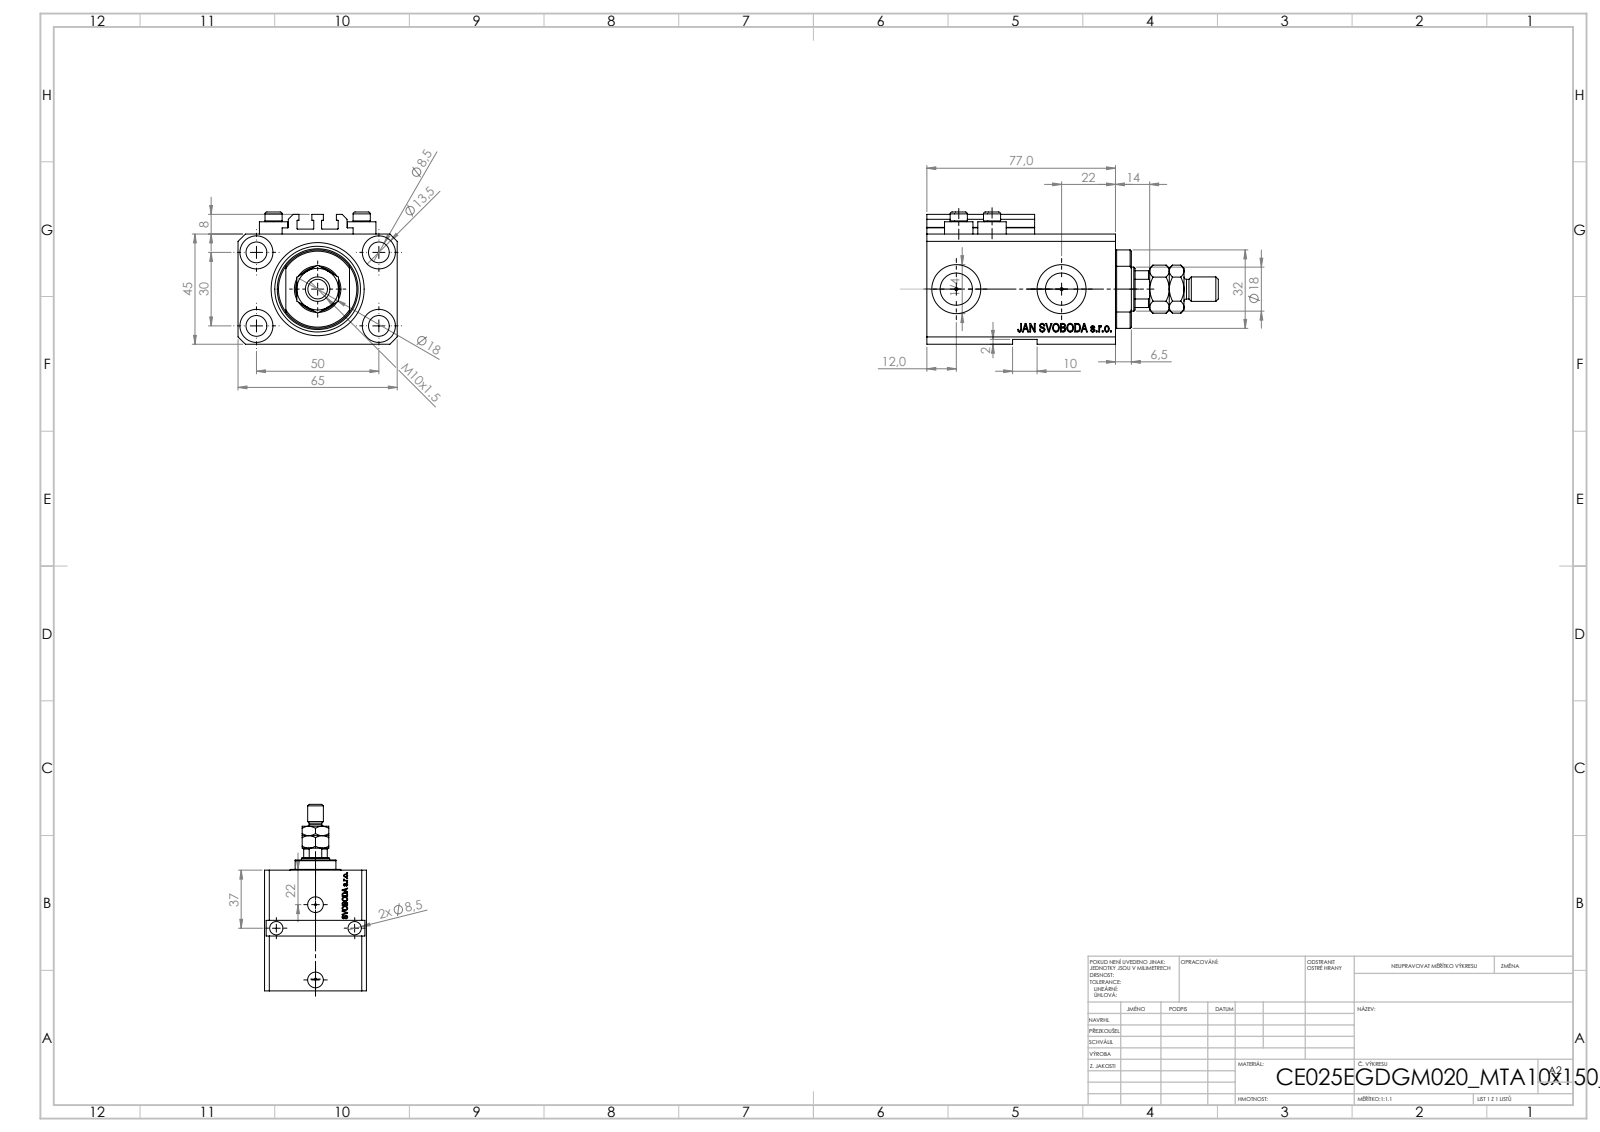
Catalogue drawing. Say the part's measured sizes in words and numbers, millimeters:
The part is named "MTA; ALLEN BOLT V250CE; V250CE_C_VCP; V250CE_VC_E (+1 more)". Its 3-D file was written by "SolidWorks 2019 (CONFIG_CONTROL_DESIGN)". It is 9 solids with 1132 faces: 530 planar, 142 cylindrical and 460 other. Overall it measures 119 by 65 by 54 millimeters. Its volume is 200 645 cubic millimeters and its surface area 62 060 square millimeters. Round holes: 7 of diameter 8.5, 4 of diameter 1.25, 4 of diameter 4, 4 of diameter 13.5, 2 of diameter 10, 2 of diameter 13.16, 2 of diameter 20, 1 of diameter 18, 1 of diameter 25, 1 of diameter 38. Round bosses or shafts: 4 of diameter 11.6, 4 of diameter 7, 1 of diameter 10, 1 of diameter 8. Partial cylindrical surfaces (rounded edges, fillets, slot ends): 10 of radius 0.2, 1 of radius 8.5, 1 of radius 16. The main face-to-face distances are 45, 65, 14, 63, 77, 2, 6.9, 56.1, 70.1, 20.5. The hole center spacings are 29.15, 50, 13.6, 15.12, 18.81, 18.97, 26.22, 26.61.
